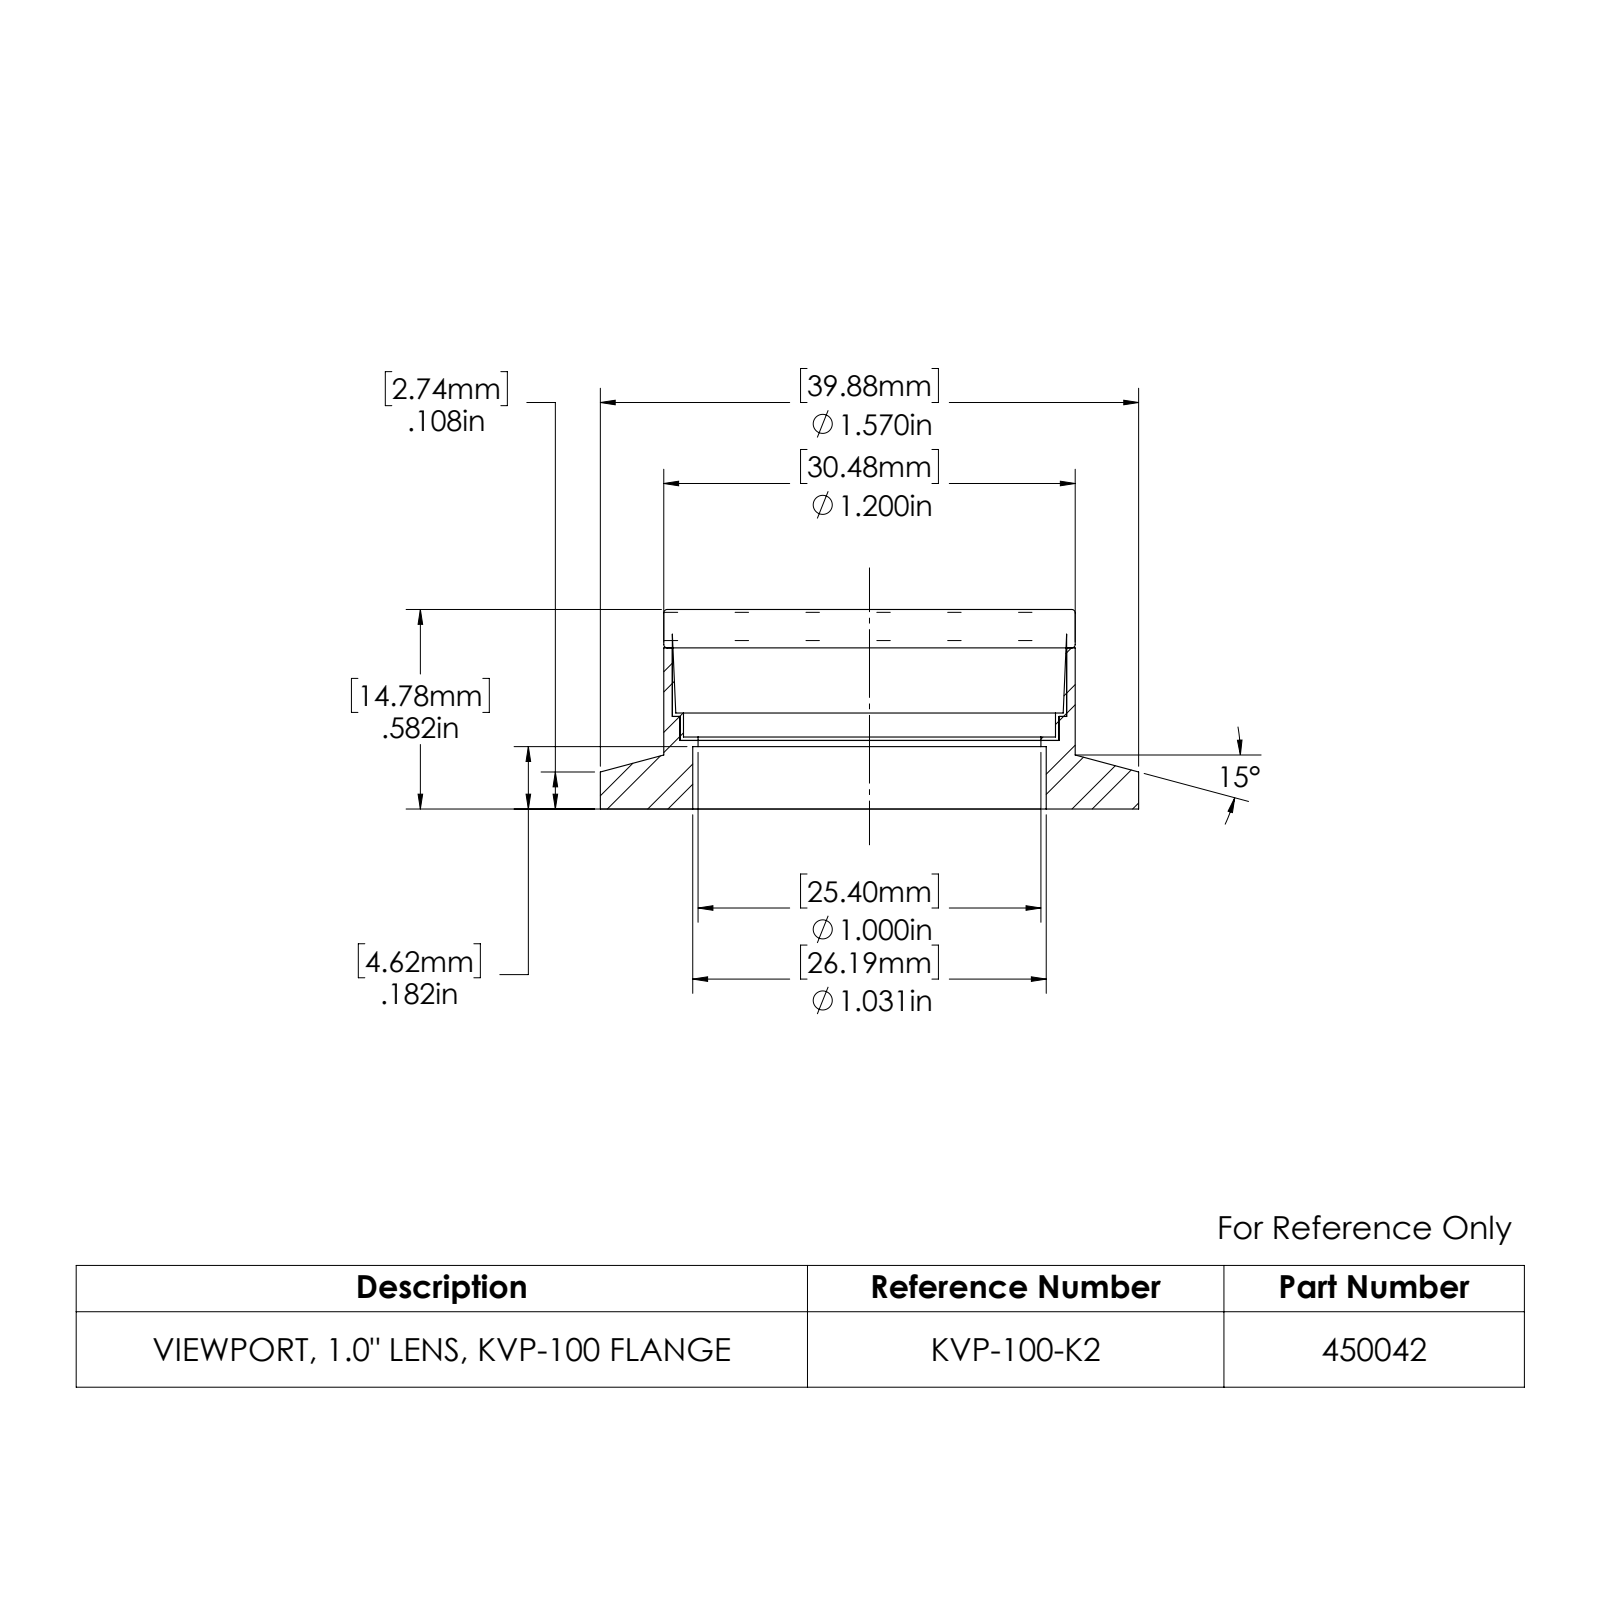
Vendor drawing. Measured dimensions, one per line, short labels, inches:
name: 450042
written by: SolidWorks 2022 (AUTOMOTIVE_DESIGN)
unit: in
bodies: 2 solids, 25 faces (7 planar, 14 cylindrical, 4 other)
size: 1.57 × 1.57 × 0.582
volume: 0.247 in³; area: 7.196 in²
holes: 1× ⌀0.9, 1× ⌀1, 1× ⌀1.031, 1× ⌀1.105, 1× ⌀1.15
bosses: 1× ⌀1.57, 1× ⌀1.2
face distances: 0.47, 0.582, 0.112, 0.2, 0.27, 0.382, 0.07, 0.312, 0.182, 0.018
